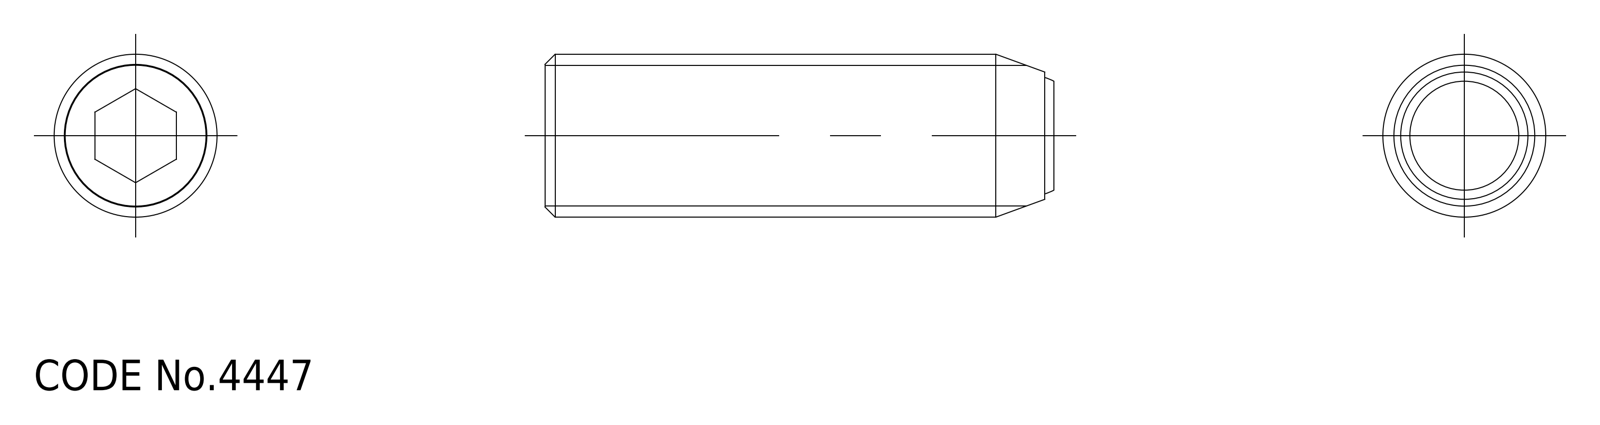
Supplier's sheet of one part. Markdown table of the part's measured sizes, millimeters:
| quantity | value |
| --- | --- |
| part name | ball; SCS_M16_50_F_16787_36 |
| STEP written by | CADfix (AUTOMOTIVE_DESIGN) |
| units | millimeters |
| bodies | 2 solids, 20 faces (0 planar, 0 cylindrical, 20 other) |
| overall size | 51.38 × 16 × 16 |
| volume | 8 808 mm³ |
| surface area | 3 796 mm² |
